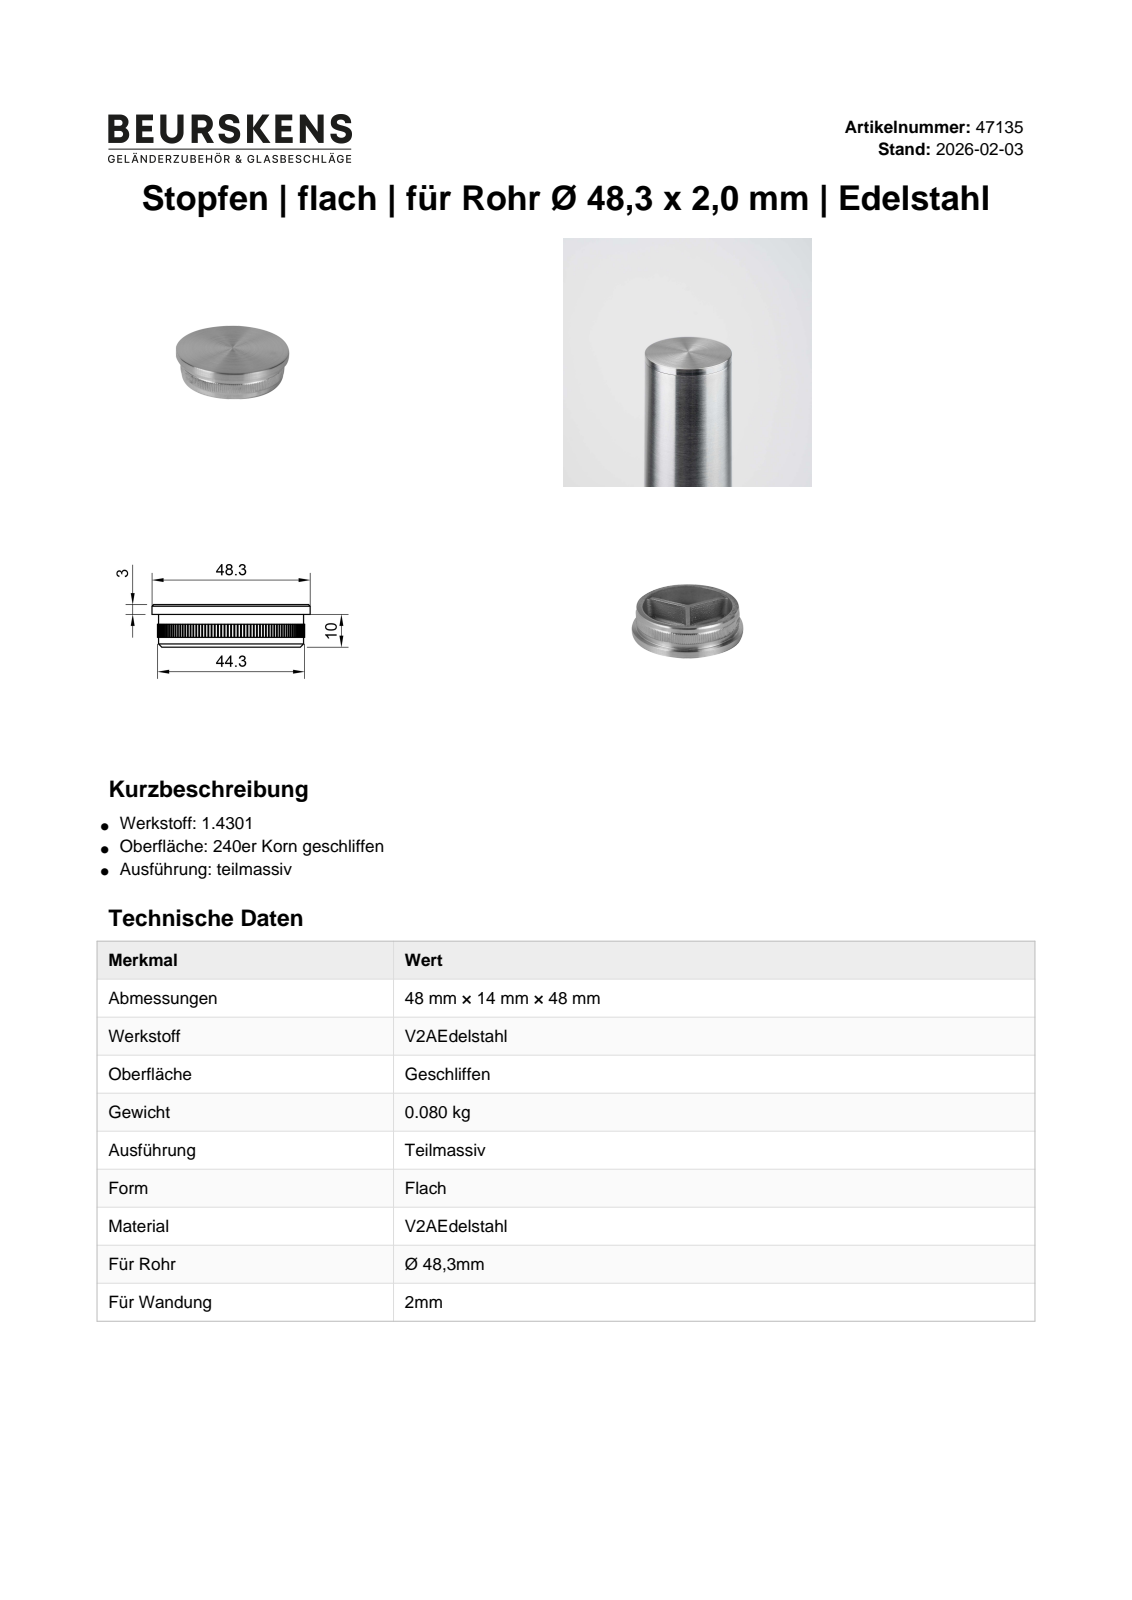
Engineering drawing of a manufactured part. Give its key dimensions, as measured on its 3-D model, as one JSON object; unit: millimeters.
{"part_name": "47135", "step_written_by": "Autodesk Inventor 2022 (AUTOMOTIVE_DESIGN)", "units": "millimeters", "bodies": {"solids": 1, "faces": 292, "planar": 6, "cylindrical": 284, "other": 2}, "overall_size": [48.3, 48.3, 13], "volume_mm3": 9636, "surface_area_mm2": 6742, "round_holes": [[38, 1]], "round_bosses_or_shafts": [[48.3, 1], [44.3, 1]], "partial_cylinders_radius": [[0.12, 140], [22.45, 1]], "face_to_face_distances": [3, 10, 13, 7, 4, 6]}
